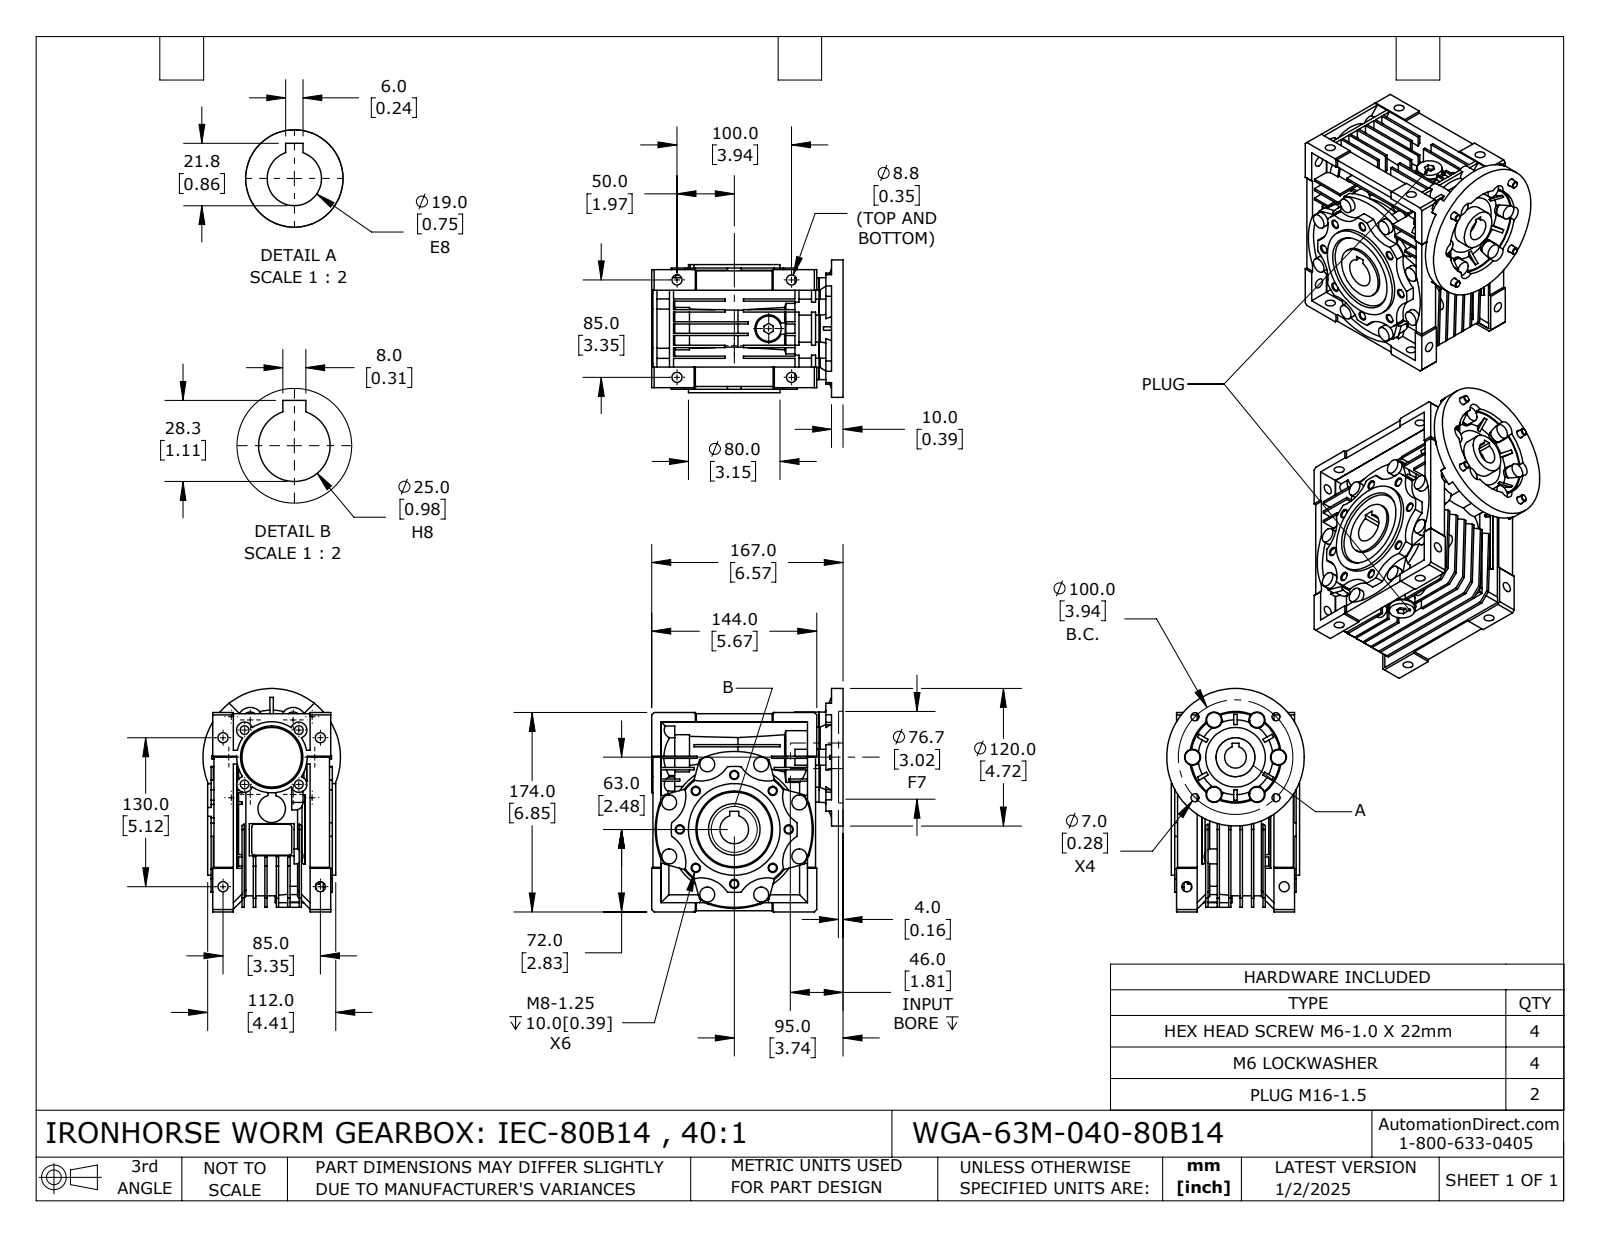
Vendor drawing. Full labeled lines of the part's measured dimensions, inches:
Part name (STEP PRODUCT): WGA-63M-040-80B14
STEP written by: SolidWorks 2024 (CONFIG_CONTROL_DESIGN)
Units: inches
Bodies: 16 solids, 1442 faces (853 planar, 413 cylindrical, 176 other)
Overall size (bounding box): 7.677 × 6.791 × 4.724
Volume: 112.7 in³ · Surface area: 542.9 in²
Round holes (diameter × count): ⌀0.262 ×8, ⌀0.346 ×8, ⌀0.24 ×4, ⌀0.276 ×4, ⌀0.298 ×4, ⌀0.571 ×2, ⌀0.748 ×1, ⌀0.787 ×1, ⌀0.984 ×1, ⌀1.339 ×1, ⌀1.457 ×1, ⌀1.772 ×1
Round bosses / shafts (diameter × count): ⌀0.512 ×14, ⌀0.551 ×6, ⌀0.48 ×4, ⌀0.236 ×4, ⌀0.945 ×3, ⌀0.866 ×2, ⌀0.622 ×2, ⌀0.539 ×2
Partial cylindrical surfaces — rounded edges, fillets, slot ends (radius × count): R0.276 ×10, R1.063 ×8, R0.275 ×6, R0.433 ×6, R0.098 ×4, R0.329 ×1, R1.161 ×1, R1.201 ×1
Main face-to-face distances: 0.394, 0.315, 0.787, 0.079, 1.181, 0.709, 0.472, 0.276, 1.575, 0.039
Hole centre spacings: 1.431, 1.87, 2.37, 2.645, 3.456, 0.65, 1.319, 1.865
